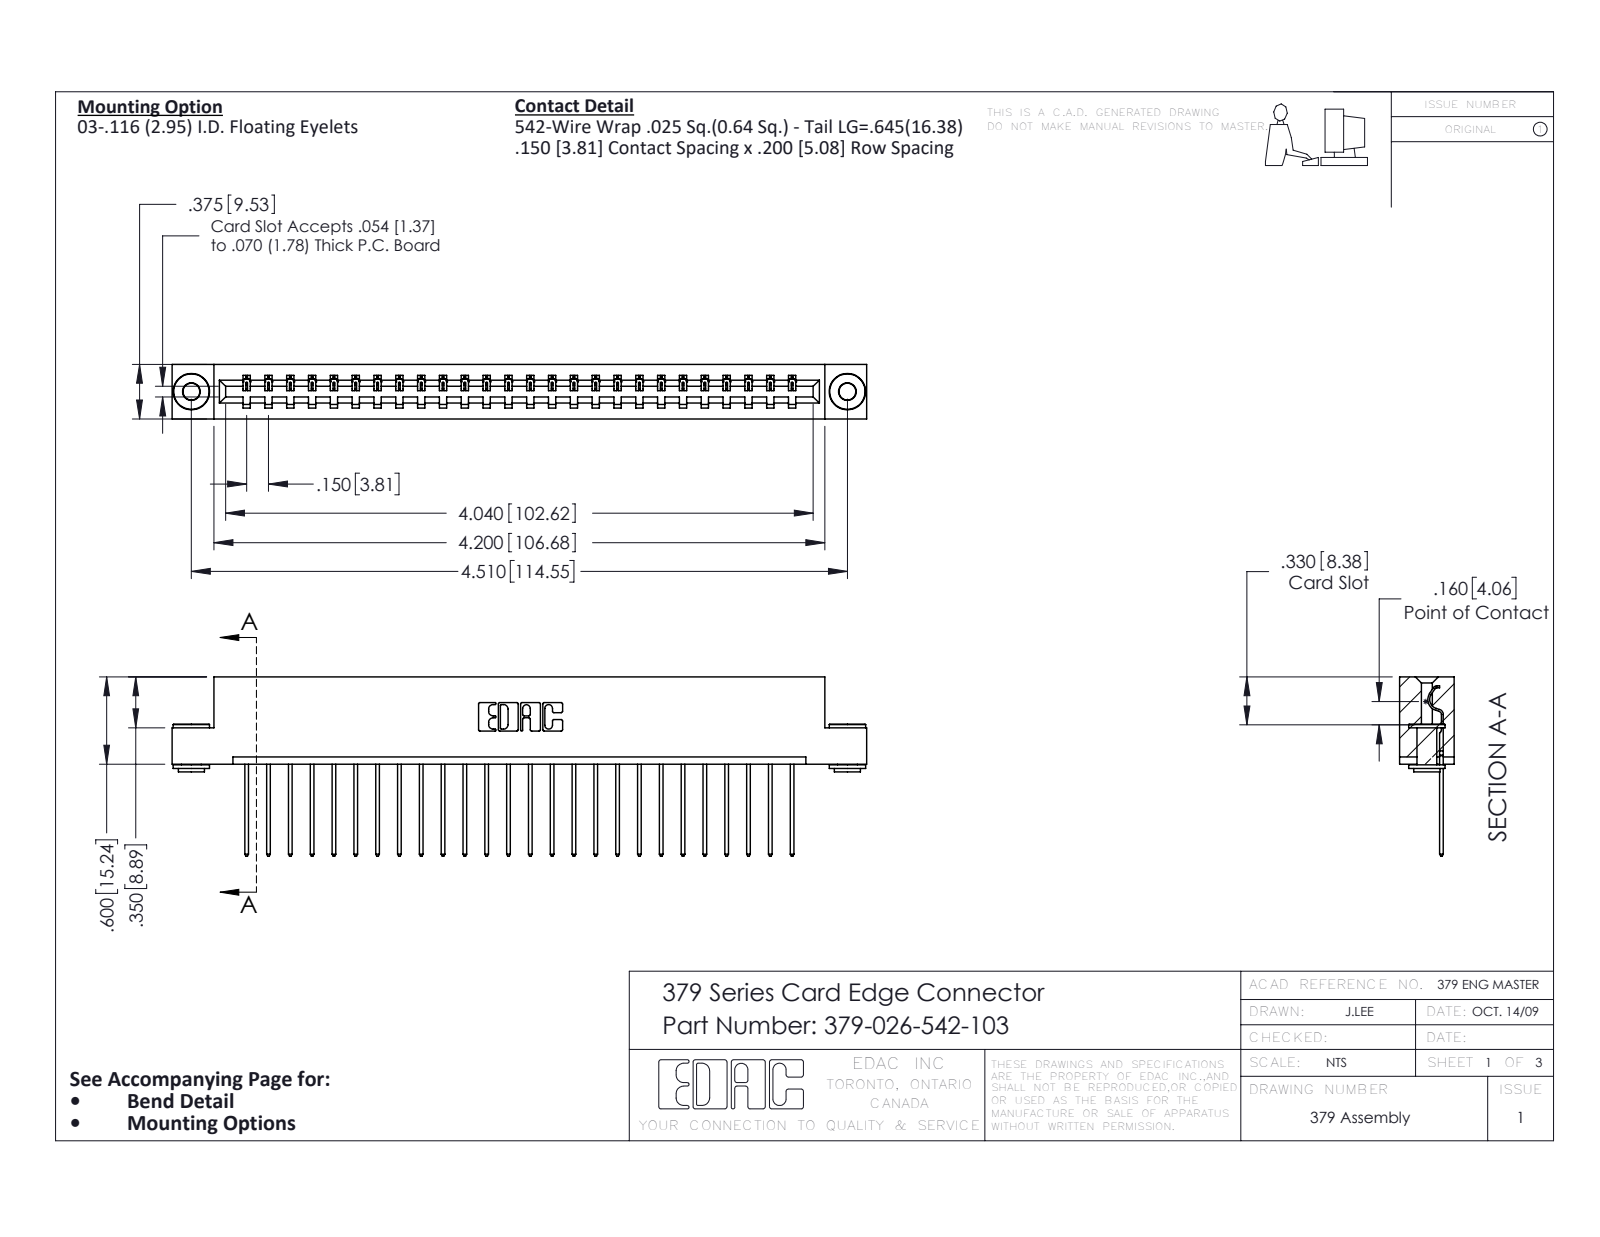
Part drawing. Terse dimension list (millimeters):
name: 345-292-001_345-293-142; 379 Part_Flush - .156 Dia - TH; 379-026-542-103; 345-250-002_345-250-002-102
written by: SolidWorks 2016 (CONFIG_CONTROL_DESIGN)
unit: mm
bodies: 29 solids, 1660 faces (1172 planar, 480 cylindrical, 8 other)
size: 121.3 × 31.3 × 9.5
volume: 12 600 mm³; area: 13 460 mm²
holes: 2× ⌀2.9, 2× ⌀4
bosses: 2× ⌀6.4, 2× ⌀4.6, 2× ⌀3.5
rounds: 52× R0.2, 52× R0.3, 22× R0.3, 6× R0.2, 6× R0.8, 3× R0.7, 1× R0.4, 1× R0.6
face distances: 7.6, 1.9, 9.5, 5.7, 7, 15.2, 0.6, 5.1, 2.5, 3.8
hole spacings: 114.6
